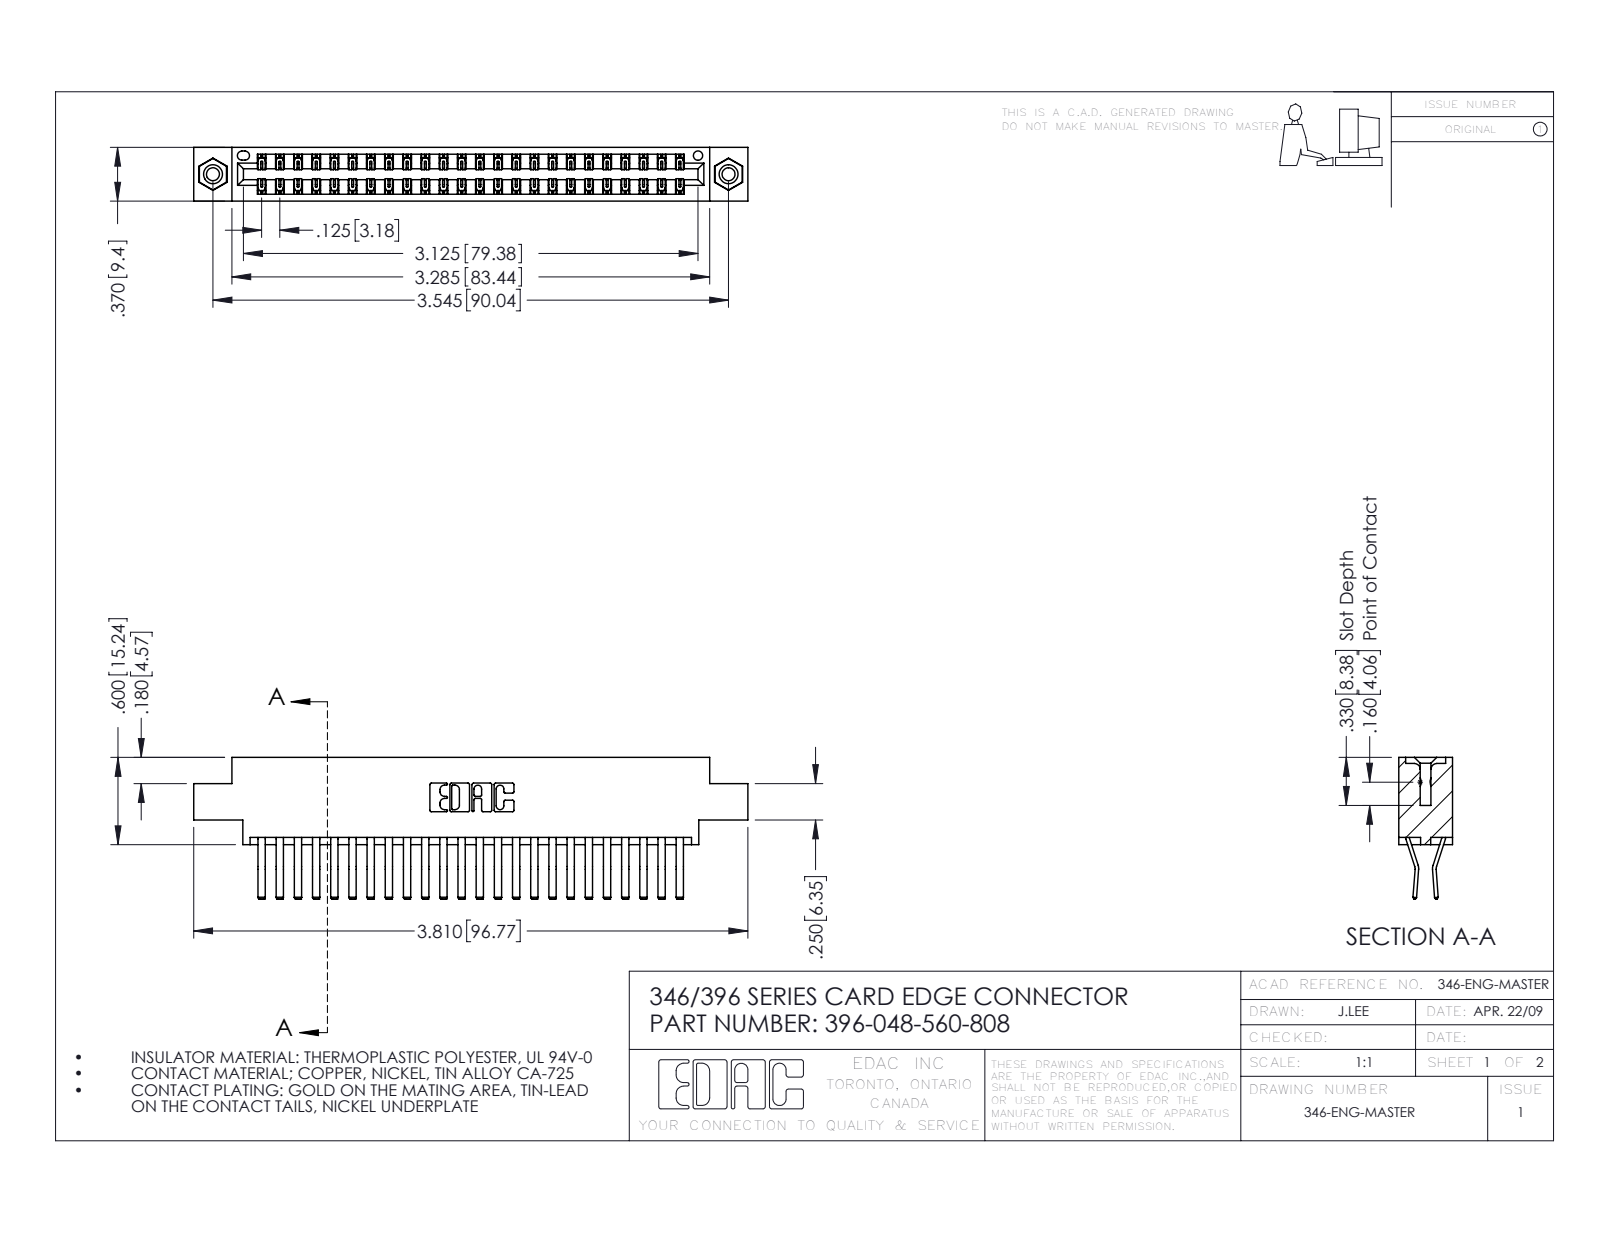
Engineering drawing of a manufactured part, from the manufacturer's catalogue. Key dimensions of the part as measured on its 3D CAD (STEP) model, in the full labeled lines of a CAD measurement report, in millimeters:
Part name (STEP PRODUCT): 346 Part_0.170 Offset - 0.156 Dia-TI; 345-250-001_345-250-003-102; 396-048-560-808; 345-292-001_560 Tail
STEP written by: SolidWorks 2016 (CONFIG_CONTROL_DESIGN)
Units: millimetres
Bodies: 51 solids, 2778 faces (1792 planar, 970 cylindrical, 16 other)
Overall size (bounding box): 96.8 × 24.8 × 9.4
Volume: 9 460 mm³ · Surface area: 13 750 mm²
Round holes (diameter × count): ⌀2.3 ×2, ⌀3.2 ×2, ⌀4 ×2, ⌀1.6 ×1
Round bosses / shafts (diameter × count): ⌀3.9 ×2
Partial cylindrical surfaces — rounded edges, fillets, slot ends (radius × count): R0.2 ×72, R0.3 ×22, R0.2 ×6, R0.8 ×6, R0.7 ×3, R0.3 ×2, R0.4 ×2, R0.6 ×2
Main face-to-face distances: 1.2, 8.2, 9.4, 0.6, 6.4, 1.8, 7.6, 7, 5.6, 3.8
Hole centre spacings: 6.2, 84.8, 90
